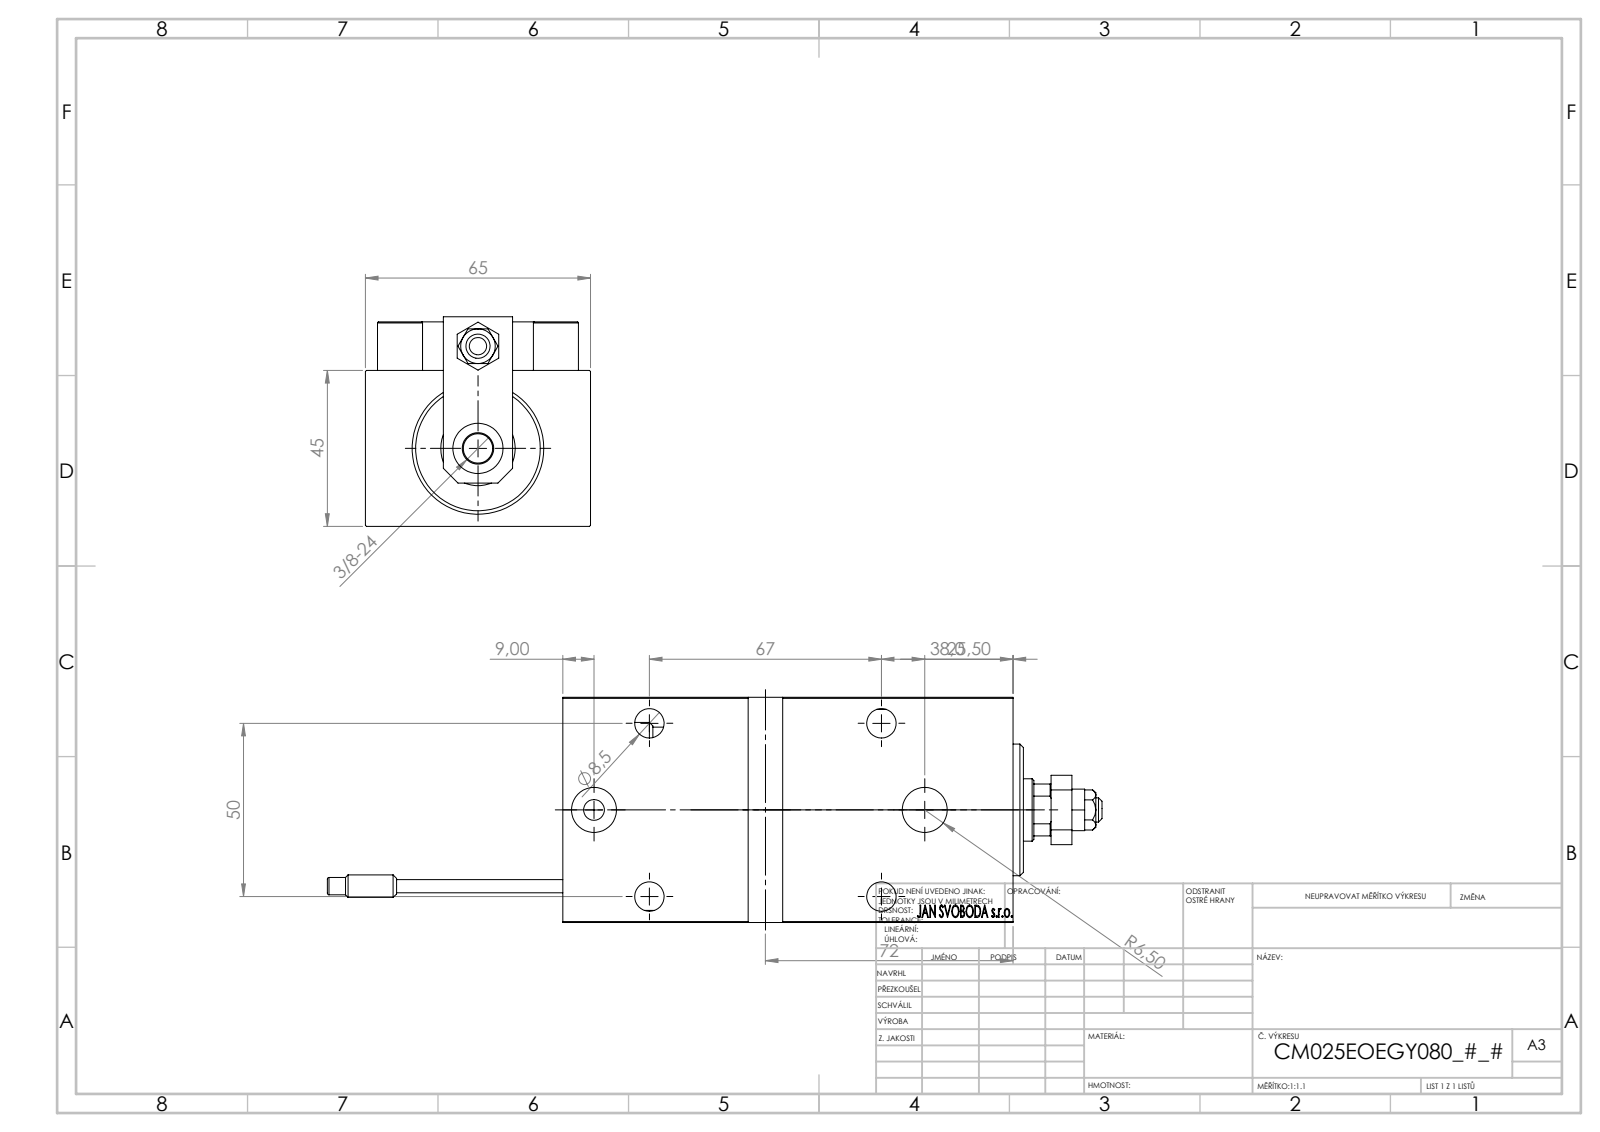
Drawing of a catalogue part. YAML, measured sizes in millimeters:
part_name: "V450CM_VC_B; Block; MAGNET; ZARAZKA (+7 more)"
step_written_by: "SolidWorks 2019 (CONFIG_CONTROL_DESIGN)"
units: millimeters
bodies: {solids: 24, faces: 1308, planar: 571, cylindrical: 184, other: 553}
overall_size: [223.7, 65, 60.5]
volume: 401003
surface_area: 89796
round_holes:
  - {diameter: 8, count: 5}
  - {diameter: 8.5, count: 5}
  - {diameter: 3.2, count: 4}
  - {diameter: 4, count: 4}
  - {diameter: 13.5, count: 4}
  - {diameter: 5, count: 2}
  - {diameter: 13, count: 2}
  - {diameter: 7, count: 1}
  - {diameter: 14.5, count: 1}
  - {diameter: 18, count: 1}
  - {diameter: 21.5, count: 1}
  - {diameter: 25, count: 1}
round_bosses_or_shafts:
  - {diameter: 5, count: 4}
  - {diameter: 6.5, count: 2}
  - {diameter: 3.8, count: 2}
  - {diameter: 38, count: 1}
  - {diameter: 27, count: 1}
  - {diameter: 13, count: 1}
  - {diameter: 11, count: 1}
  - {diameter: 6, count: 1}
partial_cylinders:
  - {radius: 0.3, count: 30}
  - {radius: 3, count: 2}
  - {radius: 8.5, count: 1}
face_to_face_distances: [45, 65, 14, 6, 59, 130, 13, 141, 3.5, 19]
hole_center_spacings: [40.31, 10.77, 11.37, 20, 21.03, 25, 27.95, 29.59]
